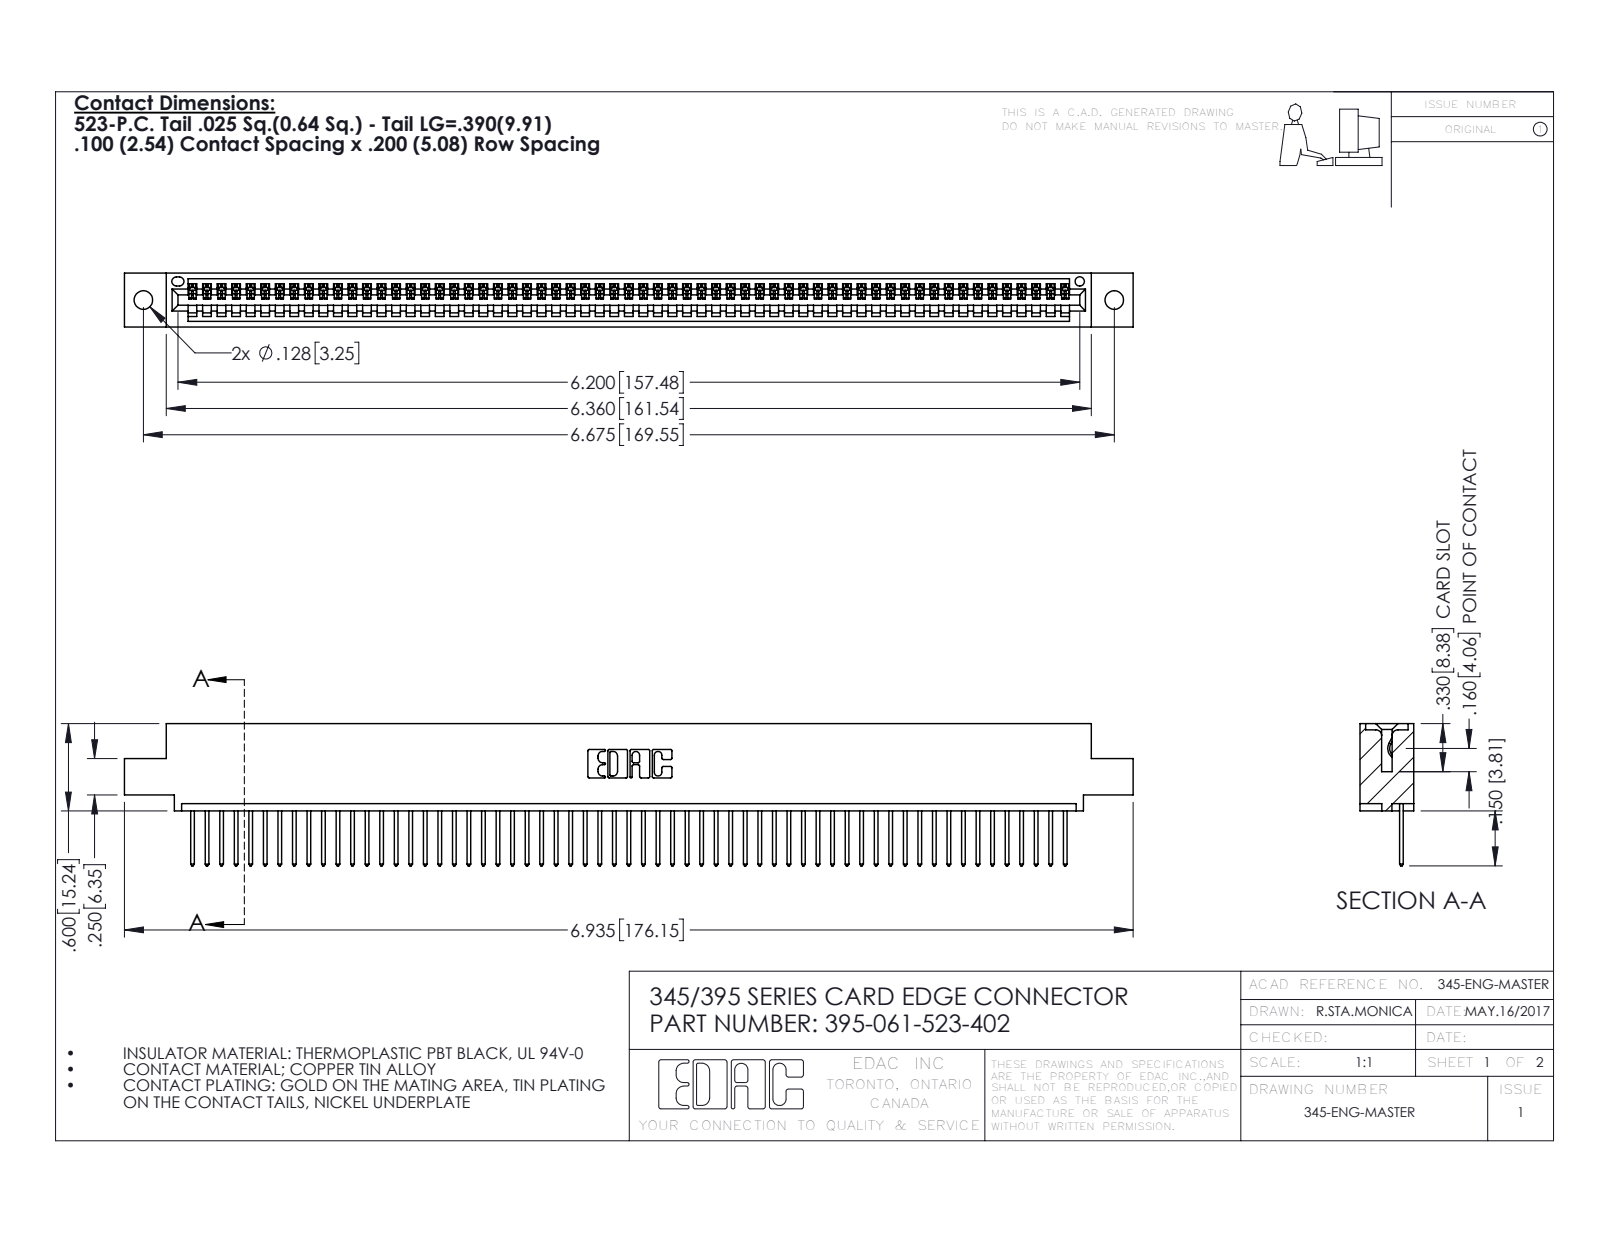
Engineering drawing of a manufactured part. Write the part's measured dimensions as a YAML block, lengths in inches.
part_name: "345-292-001_345-293-123; 345 Part_0.110 Offset - 0.128 Dia; 395-061-523-402"
step_written_by: "SolidWorks 2016 (CONFIG_CONTROL_DESIGN)"
units: inches
bodies: {solids: 62, faces: 3668, planar: 2524, cylindrical: 1144, other: 0}
overall_size: [6.935, 0.977, 0.37]
volume: 1.022
surface_area: 34.72
round_holes:
  - {diameter: 0.128, count: 2}
  - {diameter: 0.064, count: 1}
partial_cylinders:
  - {radius: 0.006, count: 122}
  - {radius: 0.01, count: 122}
  - {radius: 0.01, count: 22}
  - {radius: 0.007, count: 6}
  - {radius: 0.031, count: 6}
  - {radius: 0.026, count: 3}
  - {radius: 0.031, count: 2}
  - {radius: 0.04, count: 2}
face_to_face_distances: [0.298, 0.072, 0.37, 0.098, 0.272, 0.025, 0.2, 0.225, 0.149, 0.072]
hole_center_spacings: [0.27, 6.439, 6.675]
